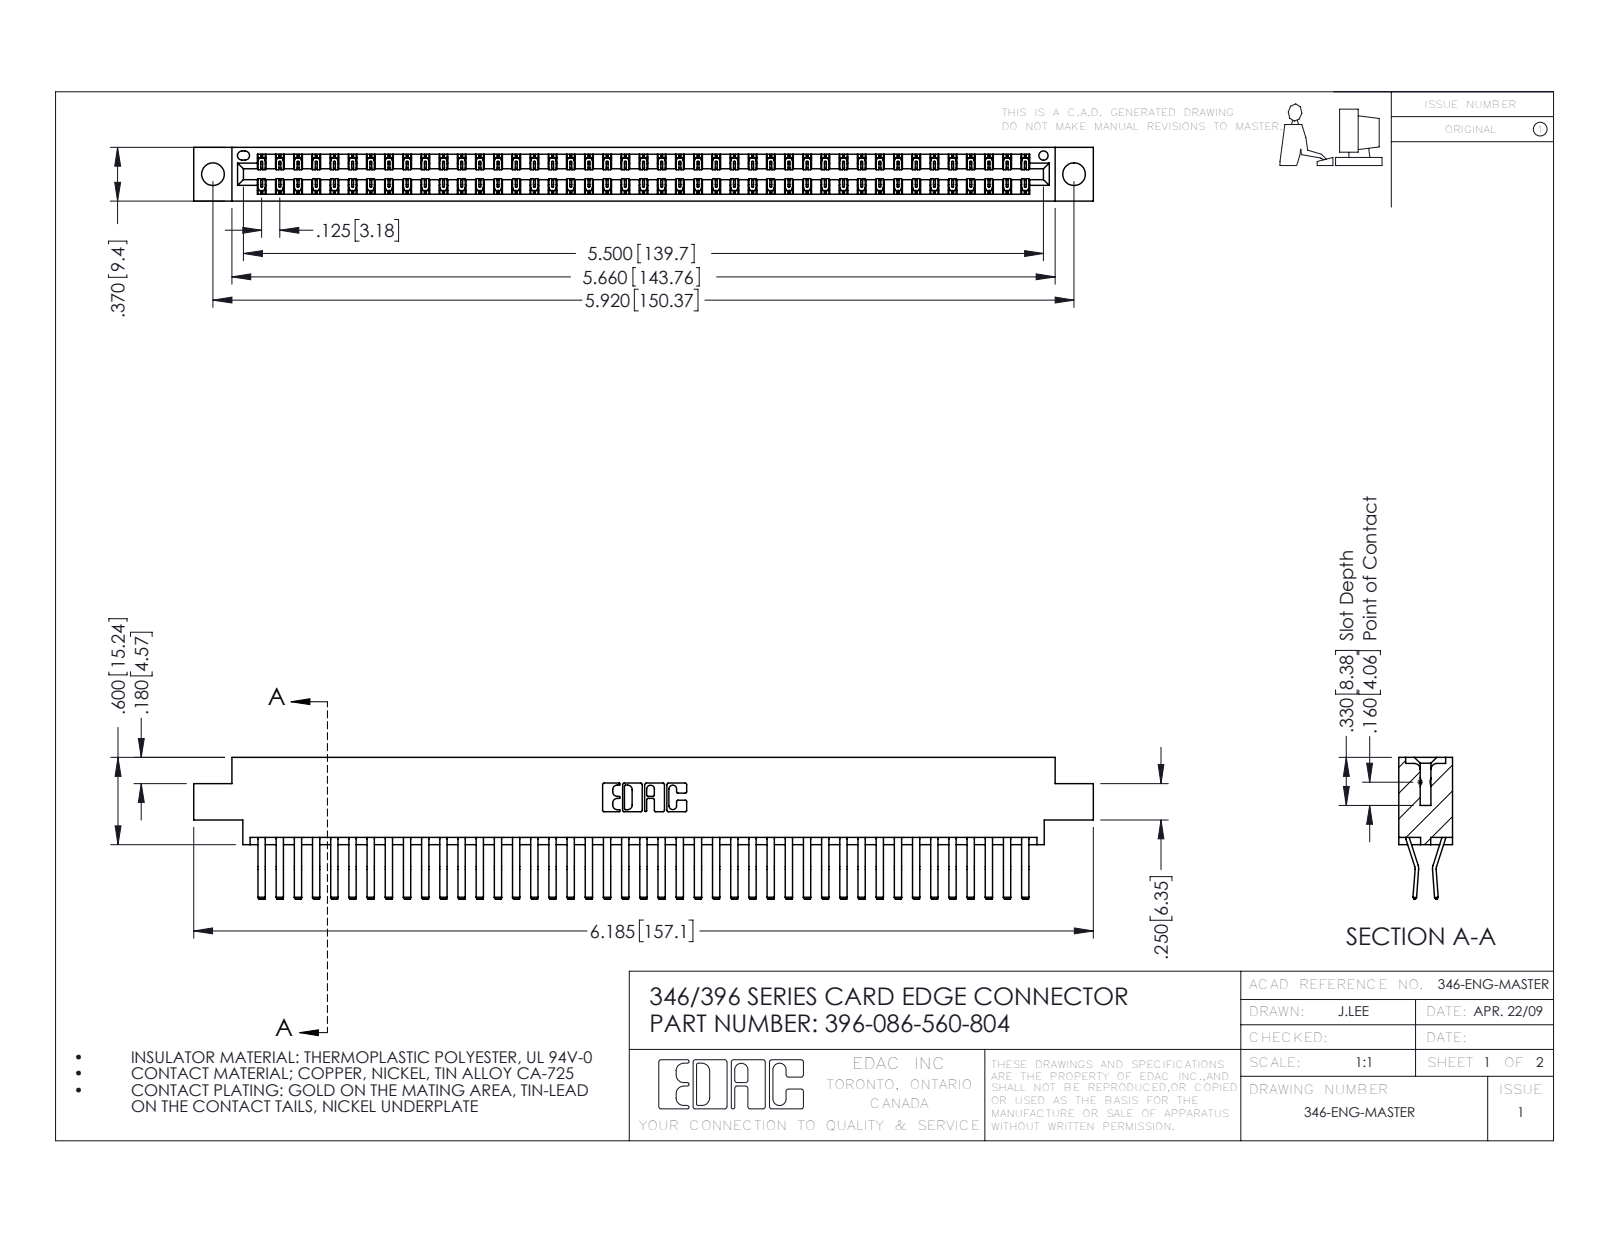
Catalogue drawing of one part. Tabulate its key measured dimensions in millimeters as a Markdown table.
| quantity | value |
| --- | --- |
| part name | 396-086-560-804; 345-292-001_560 Tail; 346 Part_0.170 Offset - 0.156 Dia-TH |
| STEP written by | SolidWorks 2016 (CONFIG_CONTROL_DESIGN) |
| units | millimeters |
| bodies | 87 solids, 4770 faces (3090 planar, 1680 cylindrical, 0 other) |
| overall size | 157.1 × 24.8 × 9.4 |
| volume | 15 600 mm³ |
| surface area | 23 020 mm² |
| round holes (diameter × count) | 4 × 2, 1.6 × 1 |
| partial cylindrical surfaces (radius × count) | 0.2 × 129, 0.3 × 22, 0.2 × 6, 0.8 × 6, 0.7 × 3, 0.3 × 2, 0.4 × 2, 0.6 × 2 |
| main face-to-face distances | 1.2, 8.2, 9.4, 0.6, 6.4, 1.8, 7.6, 7, 3.8, 5.6 |
| hole center spacings | 6.2, 145.1, 150.4 |
